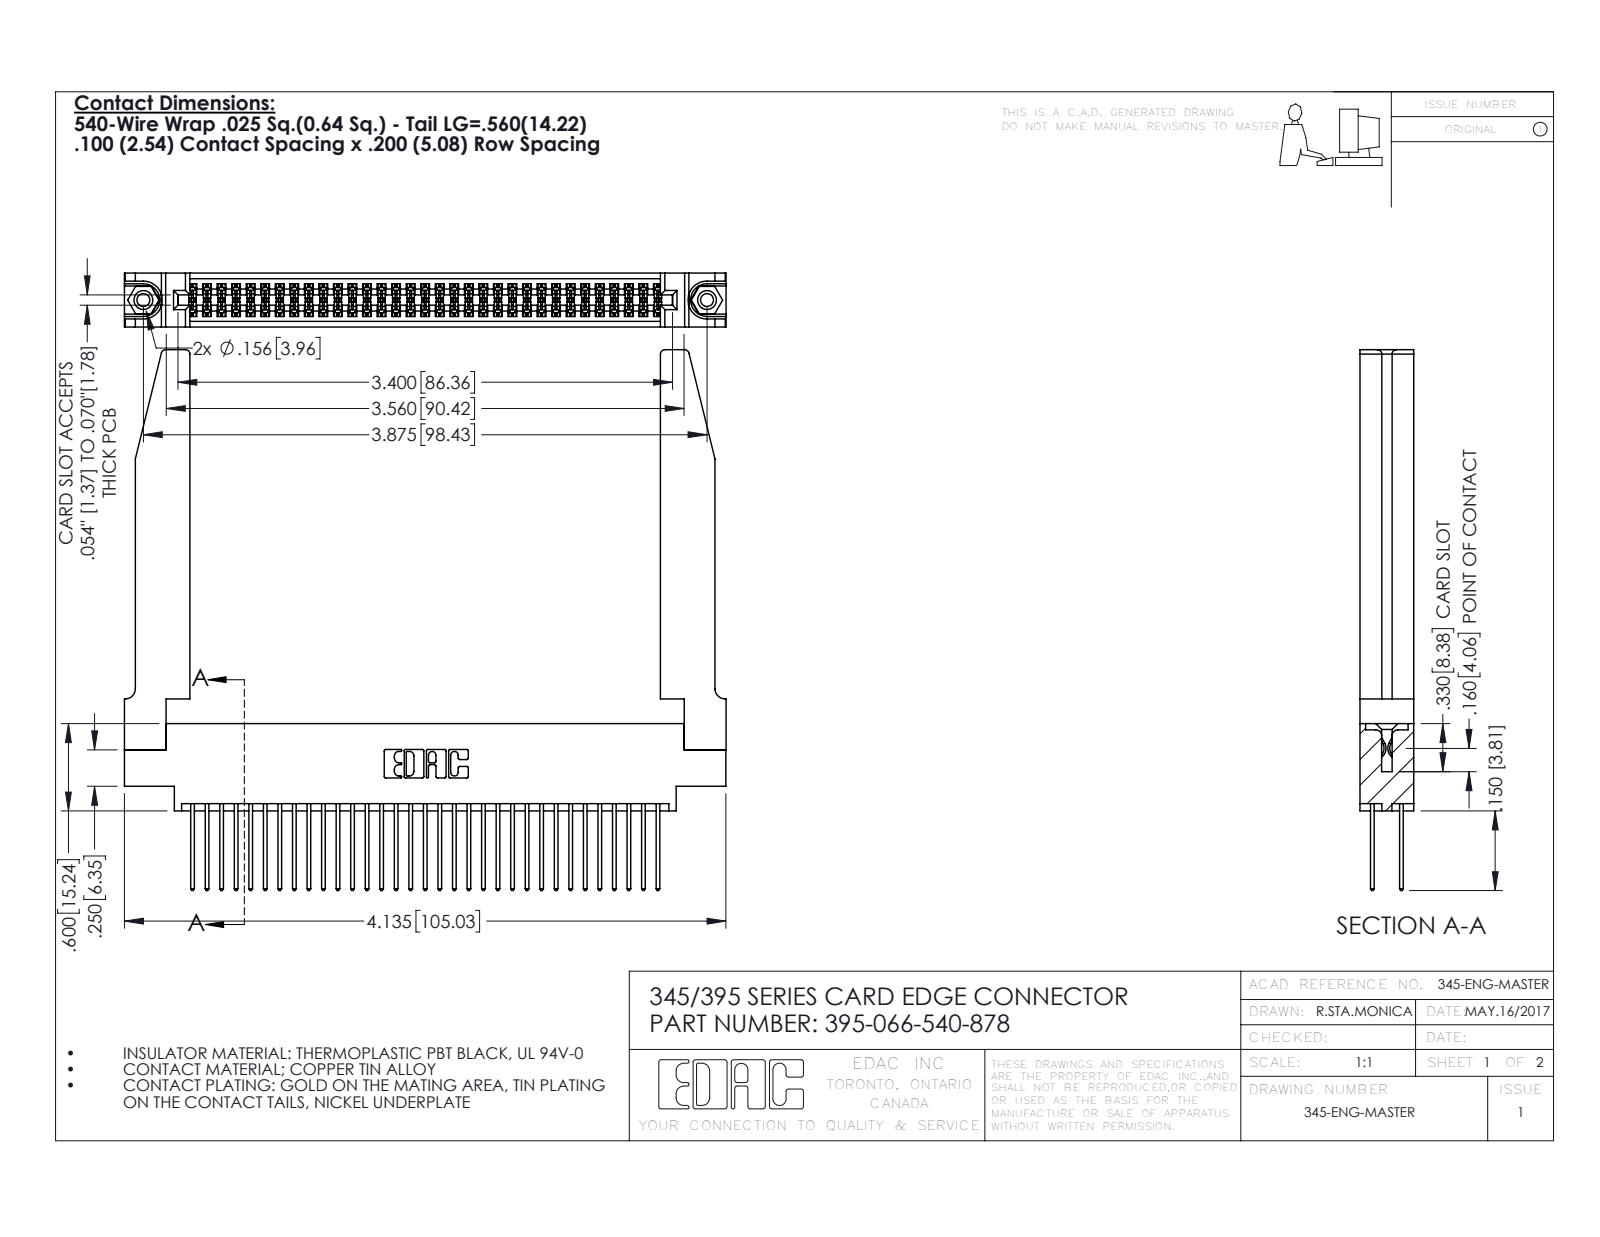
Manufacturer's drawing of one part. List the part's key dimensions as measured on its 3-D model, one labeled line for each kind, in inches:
Part name (STEP PRODUCT): 345-292-001_345-293-140; 395-066-540-878; 345-250-001_345-250-001-102; 345 Part_0.170 Offset - 0.156 Dia-TH (+1 more)
STEP written by: SolidWorks 2016 (CONFIG_CONTROL_DESIGN)
Units: inches
Bodies: 71 solids, 3664 faces (2404 planar, 1208 cylindrical, 52 other)
Overall size (bounding box): 4.136 × 3.717 × 0.37
Volume: 1.1 in³ · Surface area: 35.85 in²
Round holes (diameter × count): ⌀0.089 ×2, ⌀0.125 ×2, ⌀0.156 ×2, ⌀0.064 ×1
Round bosses / shafts (diameter × count): ⌀0.155 ×2
Partial cylindrical surfaces — rounded edges, fillets, slot ends (radius × count): R0.006 ×99, R0.01 ×66, R0.01 ×22, R0.03 ×8, R0.007 ×6, R0.031 ×6, R0.026 ×3, R0.014 ×2
Main face-to-face distances: 0.072, 0.37, 0.298, 0.098, 0.272, 0.025, 0.2, 0.225, 0.175, 0.148
Hole centre spacings: 0.27, 3.64, 3.875
